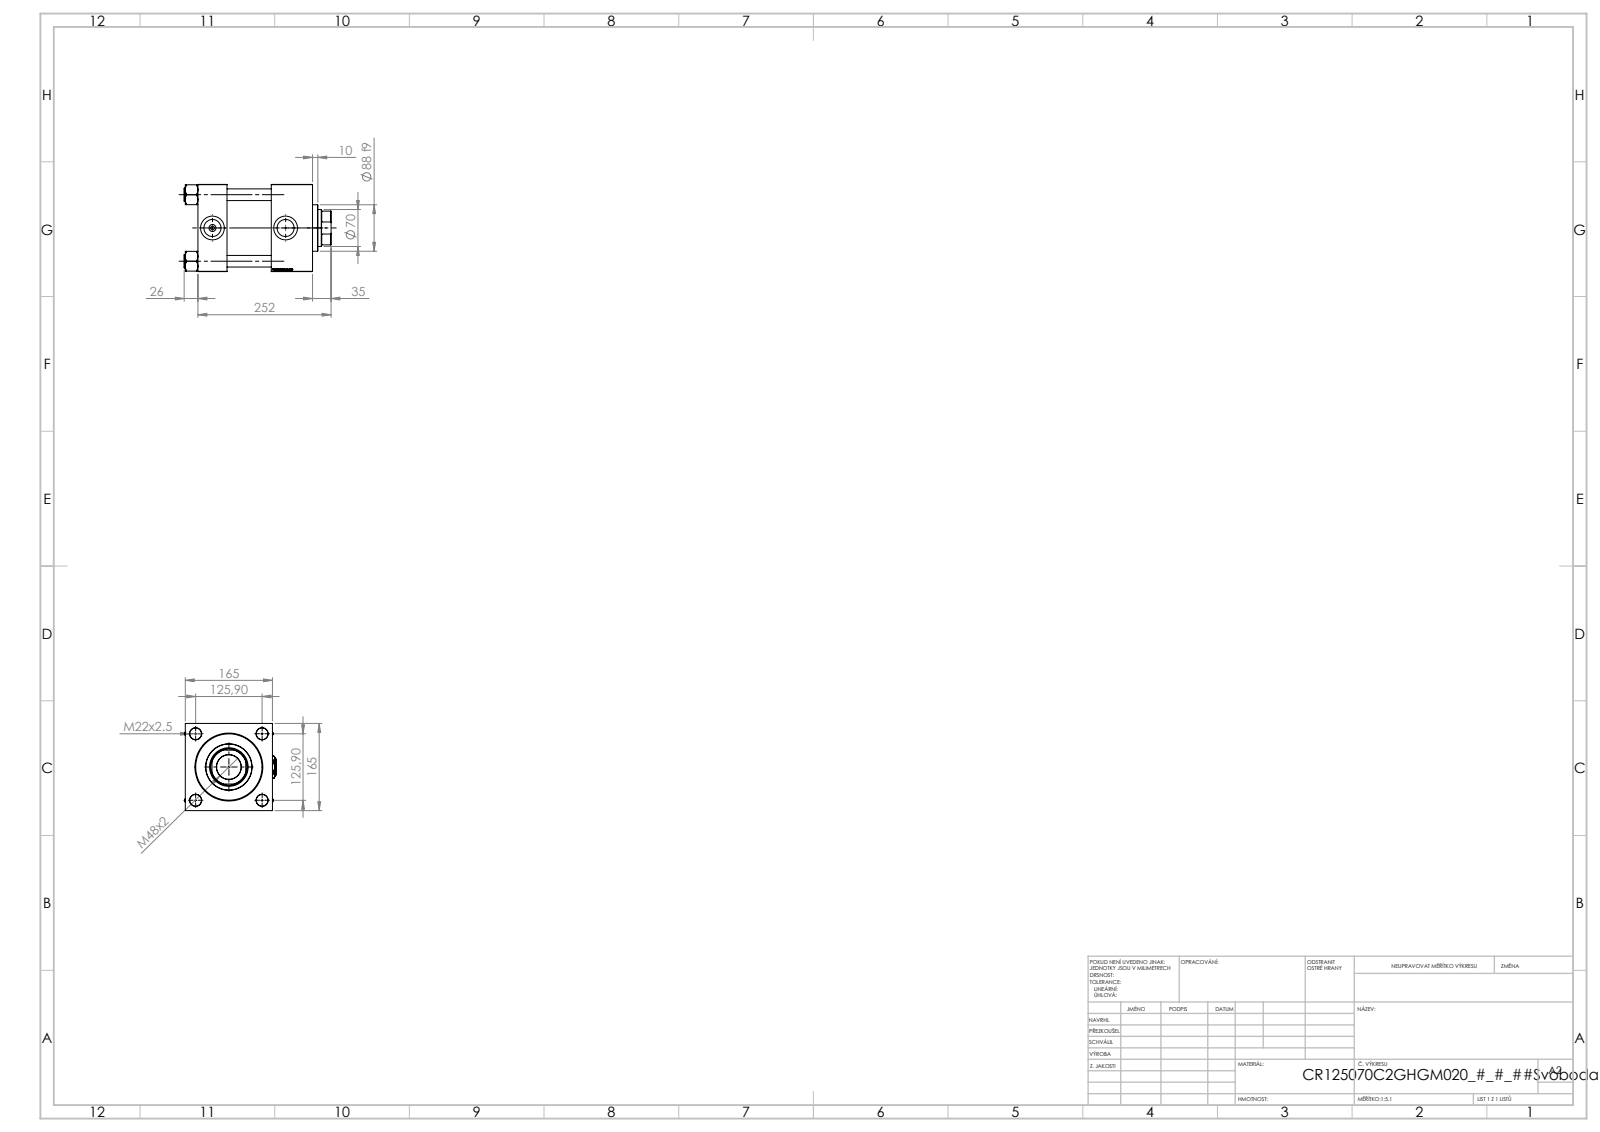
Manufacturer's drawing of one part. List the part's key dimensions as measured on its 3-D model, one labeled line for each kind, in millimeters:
Part name (STEP PRODUCT): Zatka_pro_OIL_PORT; NUT_M5_C; V215CR_C_Body; V215CR_VCP_C (+2 more)
STEP written by: SolidWorks 2019 (CONFIG_CONTROL_DESIGN)
Units: millimetres
Bodies: 12 solids, 1250 faces (598 planar, 94 cylindrical, 558 other)
Overall size (bounding box): 278 × 174.07 × 165
Volume: 4 600 000 mm³ · Surface area: 516 903 mm²
Round holes (diameter × count): ⌀22 ×4, ⌀7 ×2, ⌀32.24 ×2, ⌀45 ×2, ⌀46.5 ×1, ⌀70 ×1, ⌀73 ×1, ⌀96 ×1, ⌀125 ×1, ⌀125.5 ×1
Round bosses / shafts (diameter × count): ⌀25 ×4, ⌀131 ×1, ⌀88 ×1
Partial cylindrical surfaces — rounded edges, fillets, slot ends (radius × count): R34 ×1
Main face-to-face distances: 165, 55, 162, 217, 78, 139, 84, 188.3, 133.3, 49.3
Hole centre spacings: 89.02, 125.9, 178.05, 138.5
